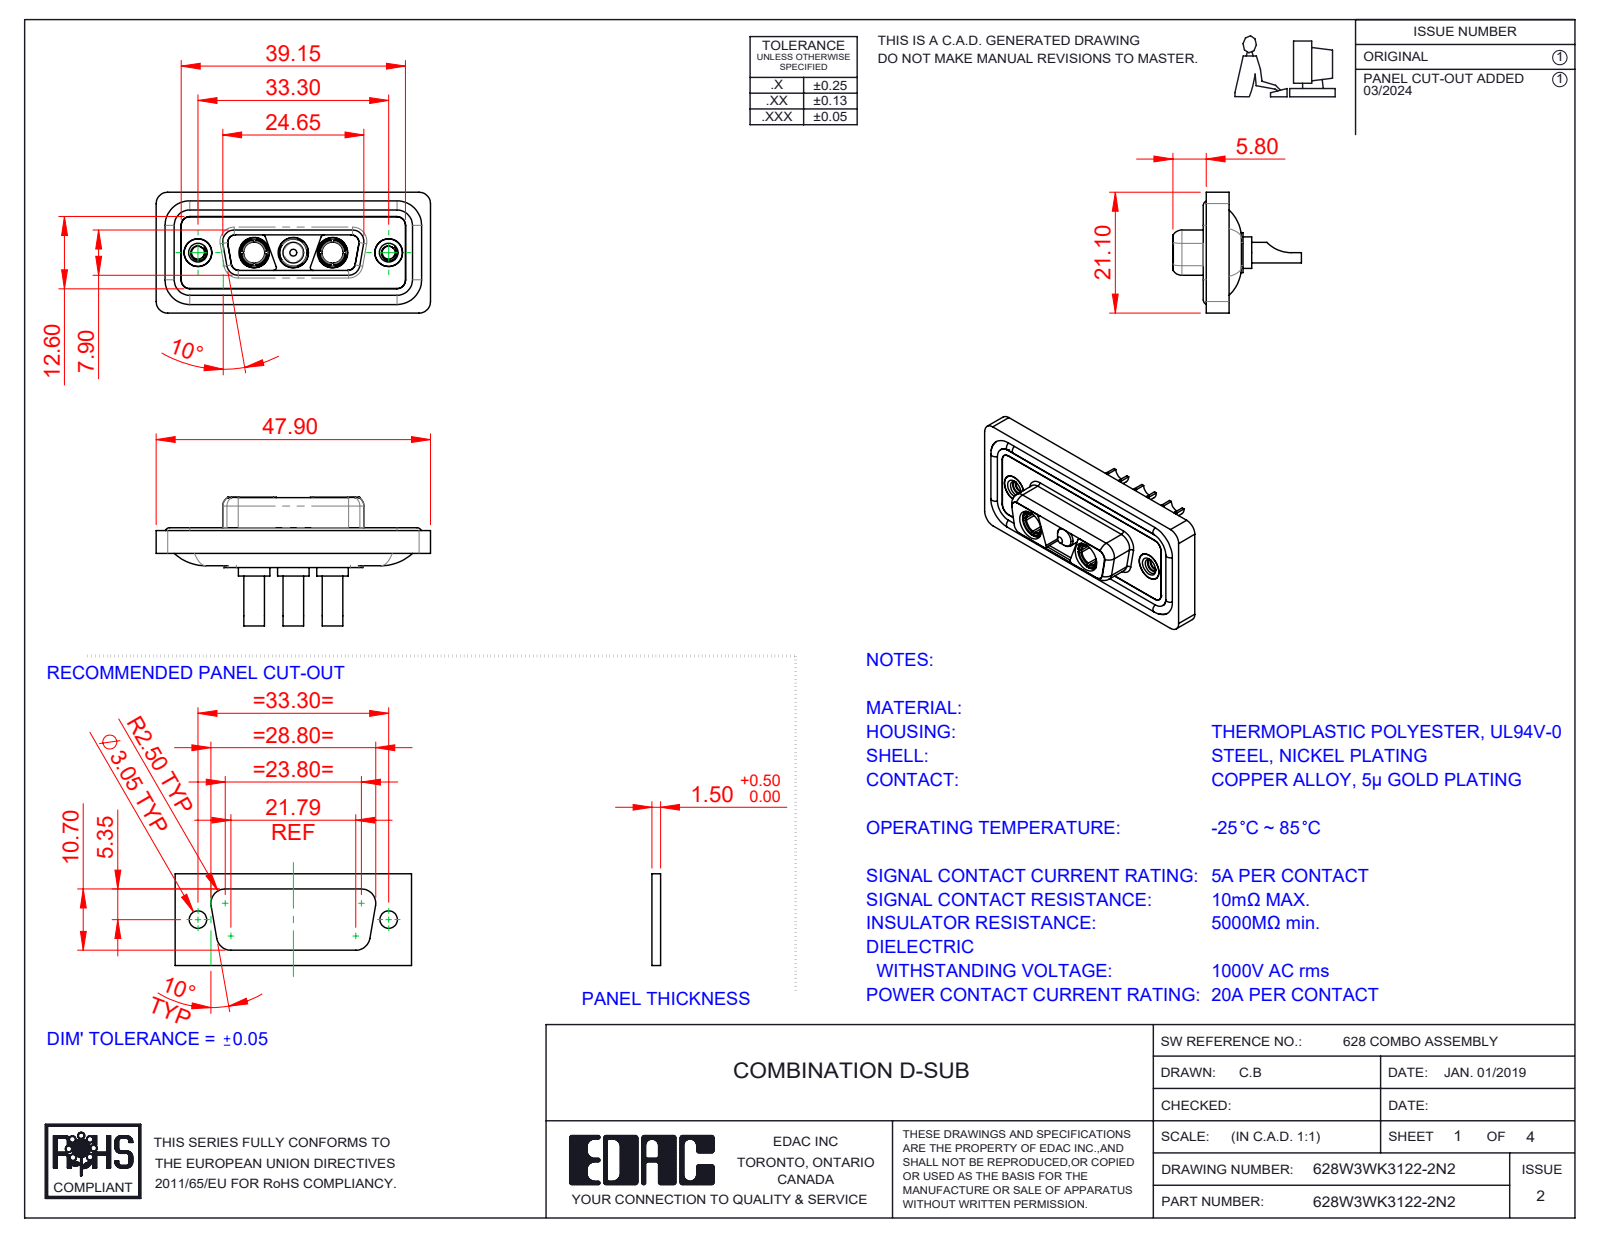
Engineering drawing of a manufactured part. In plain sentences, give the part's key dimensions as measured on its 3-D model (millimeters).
The part is named "Power Socket_20A SC; 628Combo Shell Front_15 Contacts; 628W3WK3122-2N2; 628Combo Shell Rear_15 Contacts (+4 more)". Its 3-D file was written by "SolidWorks 2023 (CONFIG_CONTROL_DESIGN)". It is 13 solids with 602 faces: 187 planar, 267 cylindrical and 148 other. Overall it measures 47.9 by 22.45 by 21.1 millimeters. Its volume is 5 916 cubic millimeters and its surface area 9 752 square millimeters. Round holes: 5 of diameter 4.85, 3 of diameter 2.7, 3 of diameter 5.3, 2 of diameter 2.26, 2 of diameter 3.7, 2 of diameter 4, 2 of diameter 4.05, 2 of diameter 5. Round bosses or shafts: 4 of diameter 1.6, 3 of diameter 5.5, 3 of diameter 5.2, 3 of diameter 4.75, 3 of diameter 3.75, 3 of diameter 3.6, 2 of diameter 4.96, 2 of diameter 4.95. Partial cylindrical surfaces (rounded edges, fillets, slot ends): 22 of radius 1.5, 20 of radius 2, 12 of radius 1.35, 8 of radius 0.5, 8 of radius 1.6, 4 of radius 0.25, 4 of radius 0.6, 4 of radius 0.65. The main face-to-face distances are 0.4, 1.6, 0.5, 1.8, 1.1, 2.9, 5.65, 7.05, 5.35, 1.5. The hole center spacings are 6.85, 9.8, 16.65, 23.5, 13.7, 33.3.
